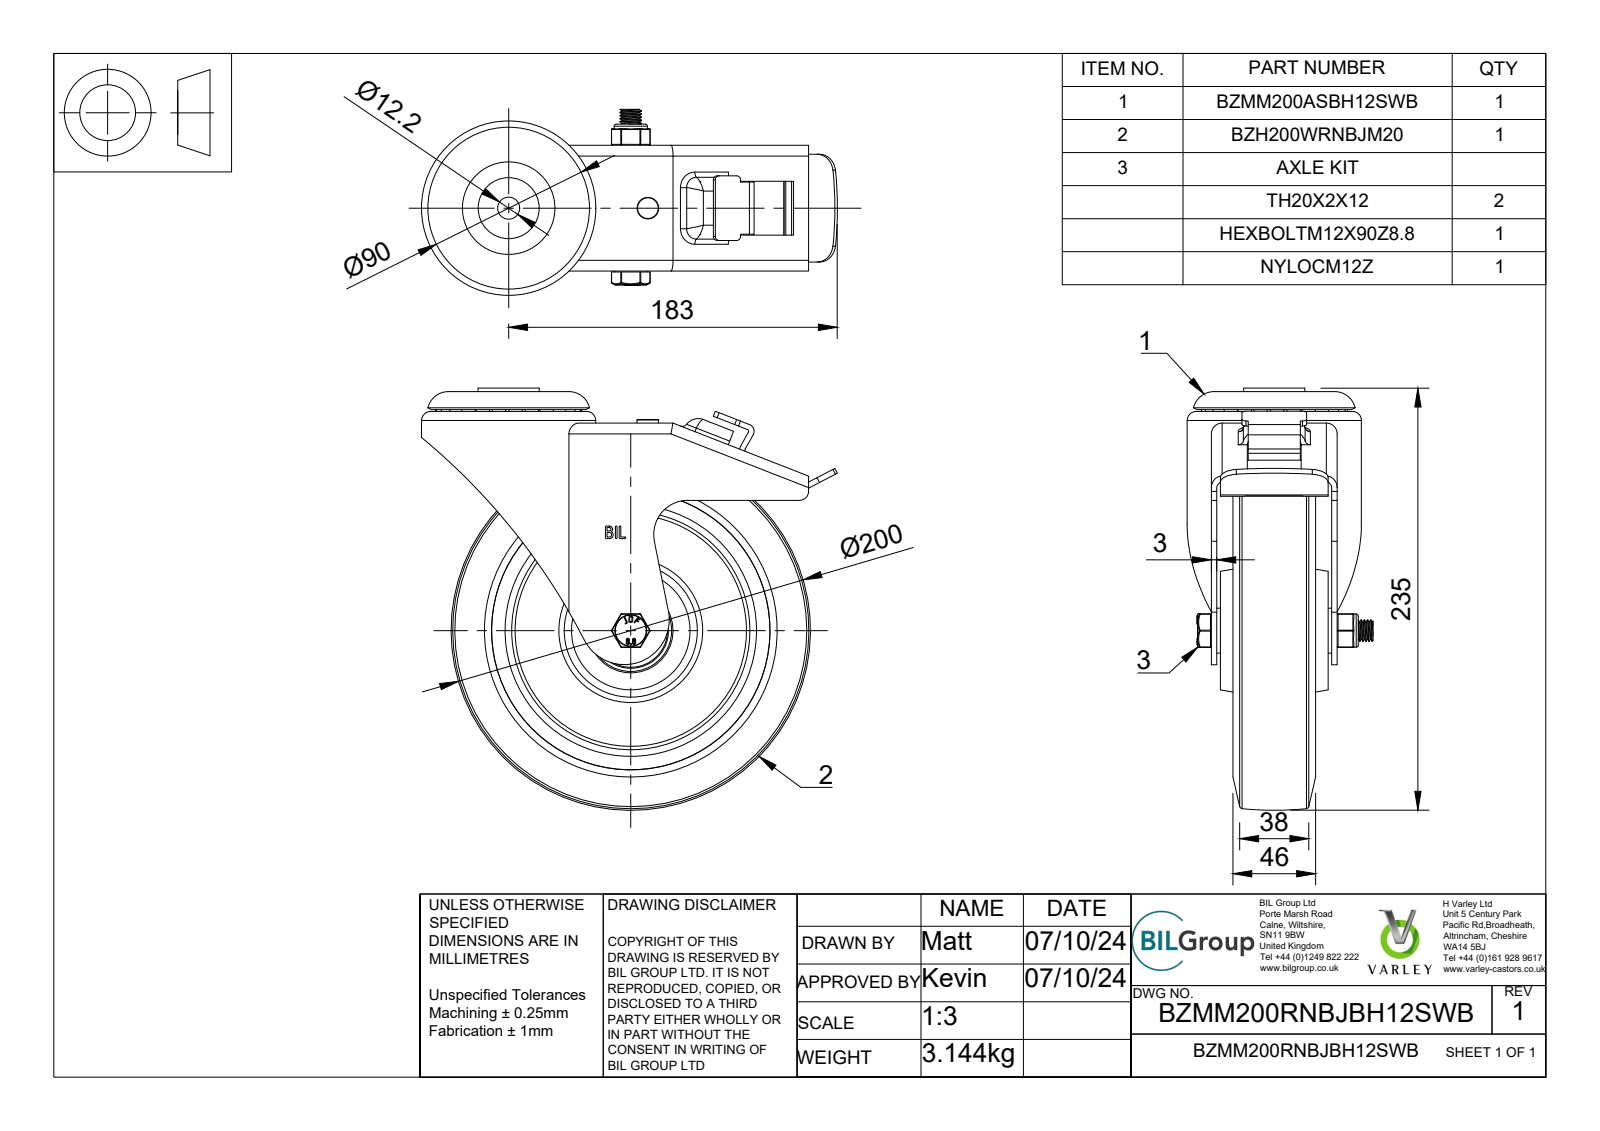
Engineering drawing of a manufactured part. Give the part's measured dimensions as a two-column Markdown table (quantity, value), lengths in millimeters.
| quantity | value |
| --- | --- |
| part name | BZMM200RNBJBH12SWB v3; BZMM200ASBH12SWB - 64 v1; ZINC PLATED, PRESSED STEEL HEAD; ZINC PLATED, PRESSED STEEL HEAD Geometry (+8 more) |
| STEP written by | Autodesk Translation Framework v13.20.0.188 (AUTOMOTIVE_DESIGN) |
| units | millimeters |
| bodies | 87 solids, 1444 faces (614 planar, 318 cylindrical, 512 other) |
| overall size | 235 × 231.5 × 103.5 |
| volume | 1 208 000 mm³ |
| surface area | 352 433 mm² |
| round holes (diameter × count) | 12.2 × 2, 6 × 1, 7 × 1, 10 × 1, 12 × 1, 12.3 × 1, 14 × 1, 20 × 1, 28.5 × 1, 30.8 × 1, 40.3 × 1, 40.5 × 1 |
| round bosses / shafts (diameter × count) | 24 × 2, 97 × 1, 78 × 1, 40.8 × 1, 39 × 1, 34 × 1, 31.3 × 1, 27 × 1 |
| partial cylindrical surfaces (radius × count) | 1.5 × 30, 0.5 × 25, 0.25 × 12, 0.75 × 10, 2 × 10, 3 × 6, 3.25 × 6, 5 × 5 |
| main face-to-face distances | 3, 39, 12, 67, 31, 28, 36, 19, 9, 55 |
| hole center spacings | 77.5 |
